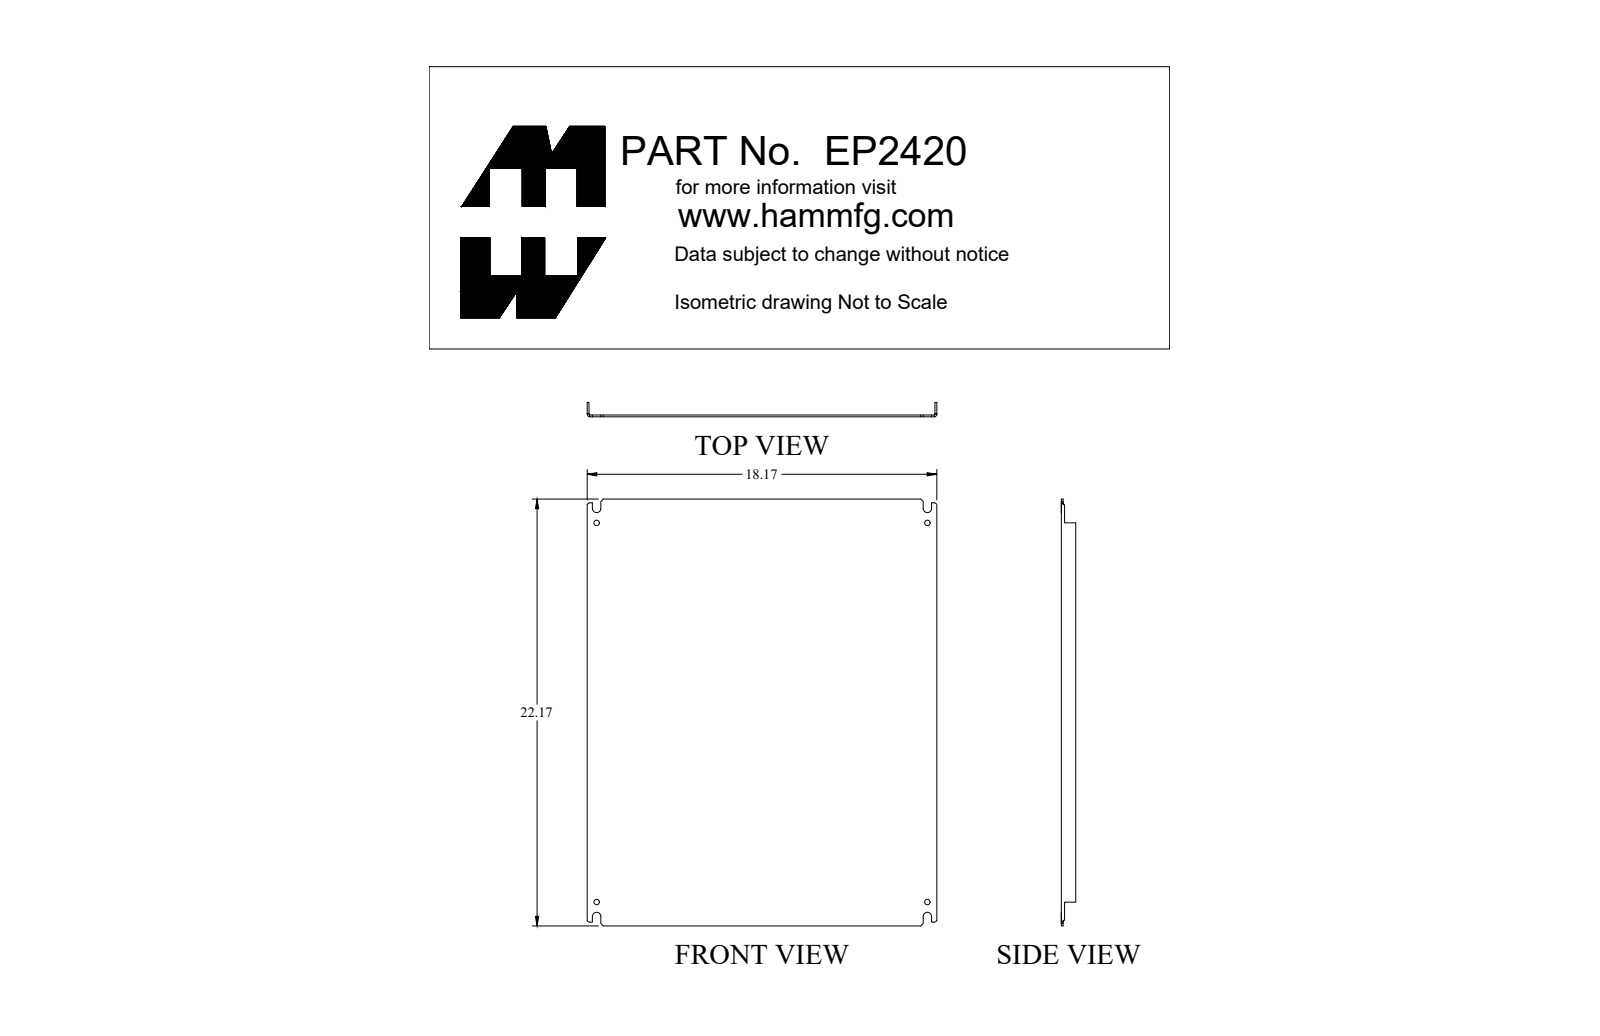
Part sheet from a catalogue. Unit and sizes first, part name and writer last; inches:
Units: inches
Overall size (bounding box): 22.17 × 18.17 × 0.75
Round holes (diameter × count): ⌀0.281 ×4
Partial cylindrical surfaces — rounded edges, fillets, slot ends (radius × count): R0.219 ×4, R0.048 ×2, R0.062 ×2, R0.143 ×2
Main face-to-face distances: 0.095, 18.075, 17.98, 18.17, 0.75, 0.655, 22.17, 0.171, 0.076, 0.579
Hole centre spacings: 17.188, 19.688, 26.135
Volume: 40.41 in³ · Surface area: 859.3 in²
Bodies: 1 solid, 84 faces (50 planar, 26 cylindrical, 8 other)
Part name (STEP PRODUCT): EP2420
STEP written by: SolidWorks 2018 (AUTOMOTIVE_DESIGN)
